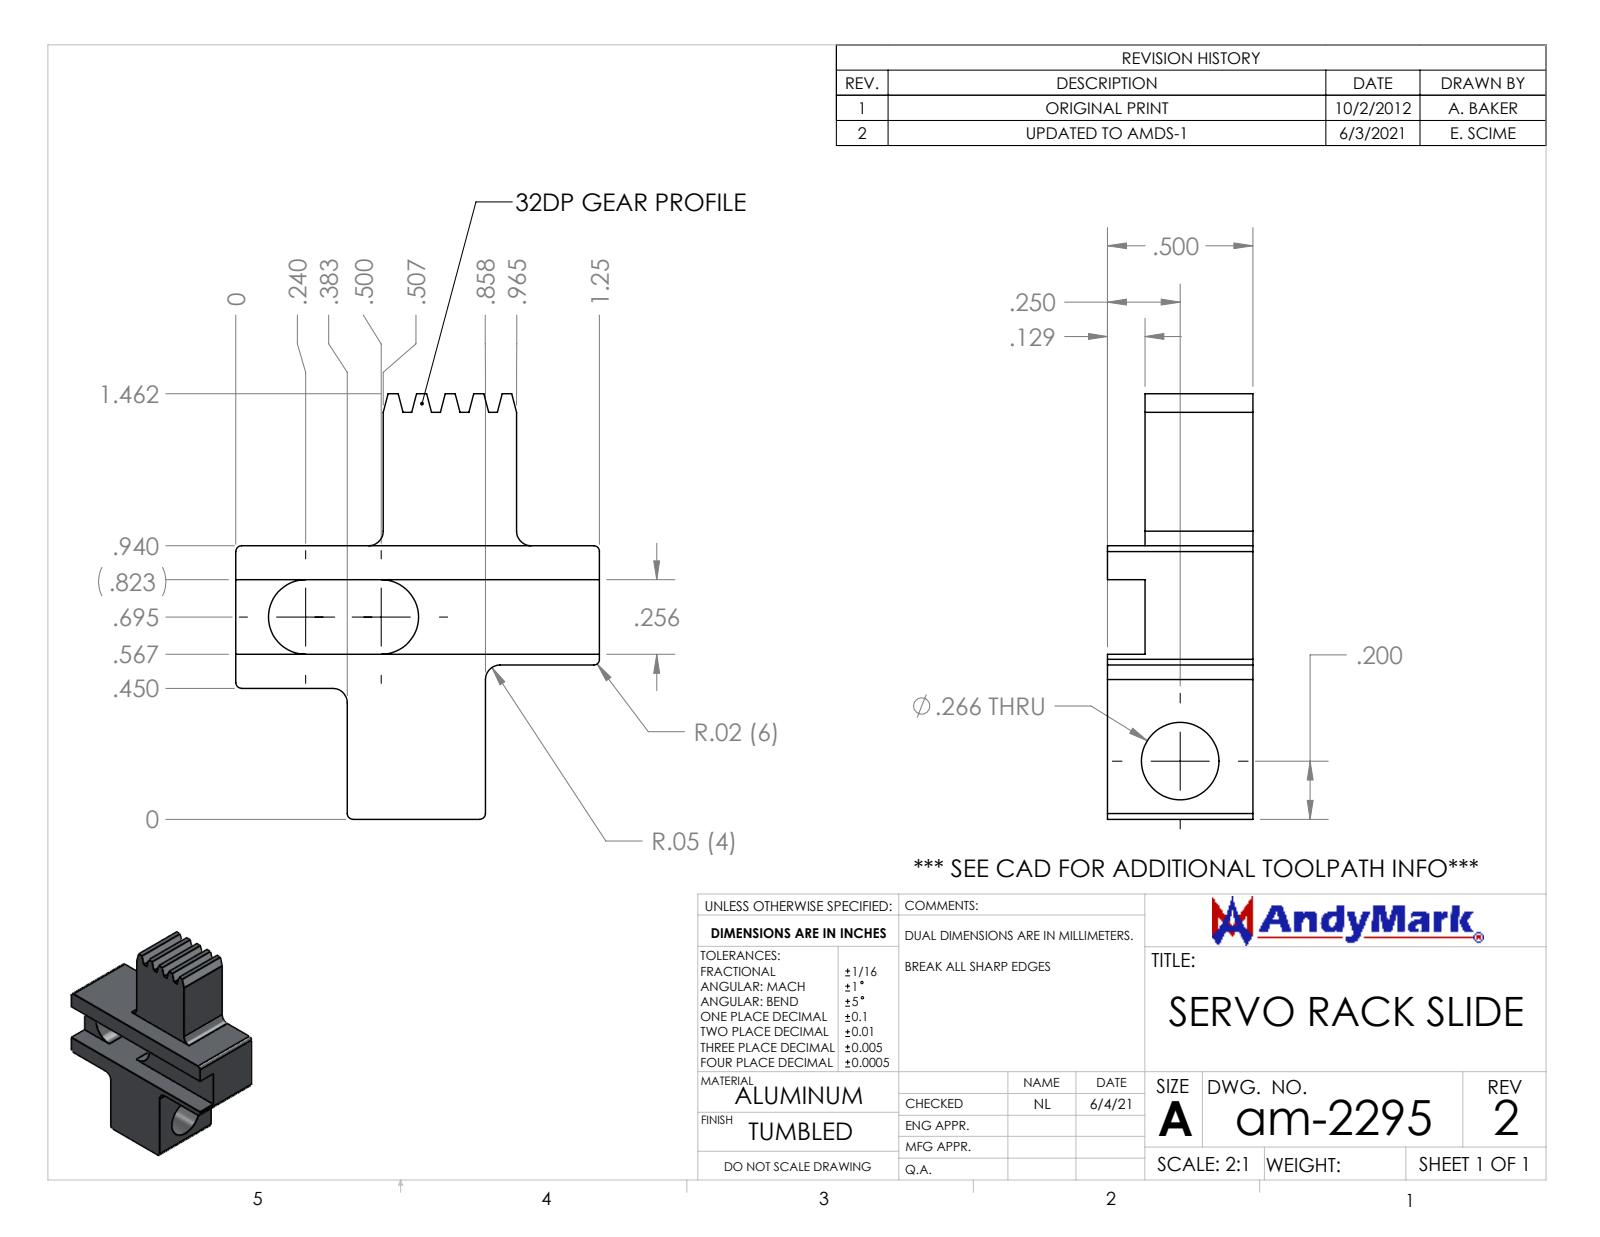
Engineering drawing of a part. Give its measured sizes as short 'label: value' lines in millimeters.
name: am-2295 Servo Rack Slide
written by: SolidWorks 2019 (CONFIG_CONTROL_DESIGN)
unit: mm
bodies: 1 solid, 52 faces (37 planar, 15 cylindrical, 0 other)
size: 37.1 × 31.8 × 12.7
volume: 6 080 mm³; area: 3 544 mm²
holes: 1× ⌀6.8
rounds: 6× R0.5, 4× R1.3, 2× R3.3
face distances: 12.7, 3.3, 9.4, 6.5, 9.5, 3, 7.2, 14.4, 20.9, 23.9
